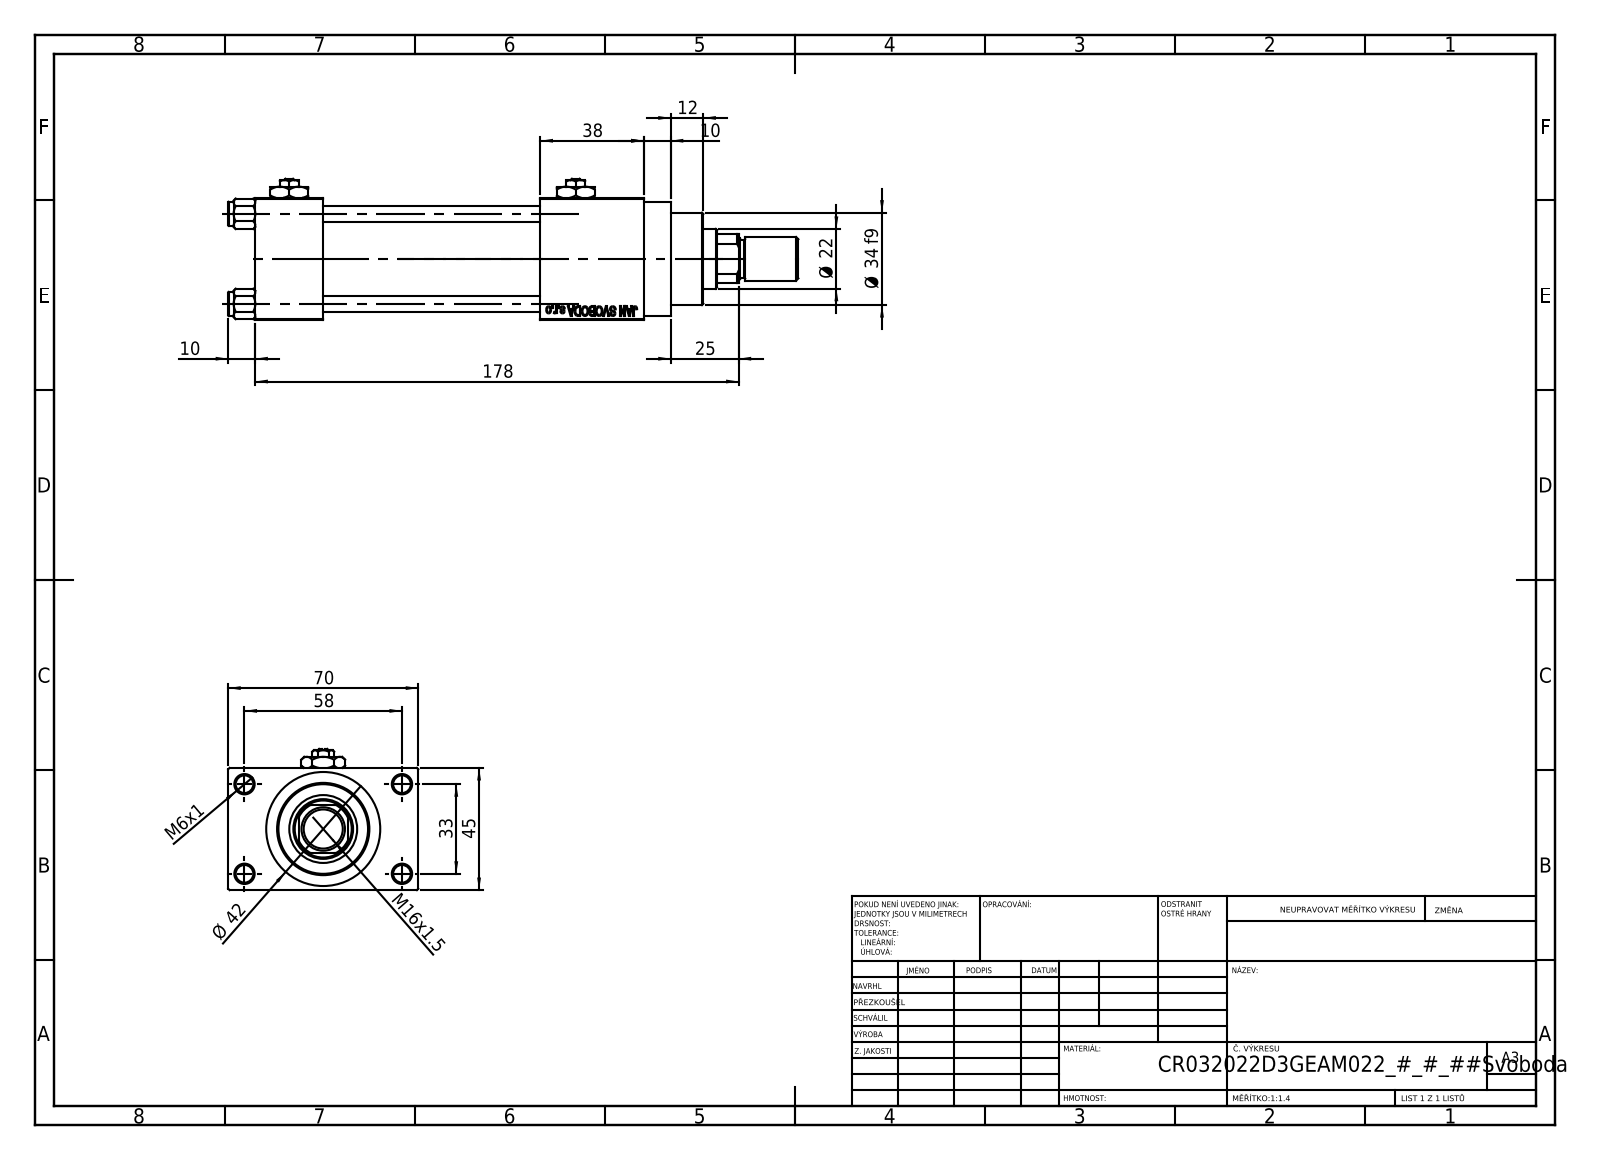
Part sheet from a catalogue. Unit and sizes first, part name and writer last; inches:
Units: inches
Overall size (bounding box): 8.268 × 2.756 × 2.047
Round holes (diameter × count): ⌀0.236 ×4, ⌀0.256 ×4, ⌀0.276 ×2, ⌀0.518 ×2, ⌀0.787 ×2, ⌀0.413 ×1, ⌀0.866 ×1, ⌀0.945 ×1, ⌀0.984 ×1, ⌀1.26 ×1, ⌀1.299 ×1
Round bosses / shafts (diameter × count): ⌀0.354 ×4, ⌀1.654 ×1, ⌀1.496 ×1, ⌀1.339 ×1, ⌀0.63 ×1, ⌀0.551 ×1
Partial cylindrical surfaces — rounded edges, fillets, slot ends (radius × count): R0.413 ×1
Main face-to-face distances: 1.772, 0.984, 0.492, 2.264, 3.15, 4.134, 4.646, 2.756, 1.496, 5.63
Hole centre spacings: 0.488, 0.924, 1.307, 1.314, 1.392, 1.795, 2.219, 1.299
Volume: 16.62 in³ · Surface area: 145.2 in²
Bodies: 14 solids, 1216 faces (546 planar, 104 cylindrical, 566 other)
Part name (STEP PRODUCT): Zatka_pro_OIL_PORT; V215CR_VCP_D; V215_VC_A; V215CR_D_TYCINKA (+3 more)
STEP written by: SolidWorks 2019 (CONFIG_CONTROL_DESIGN)
